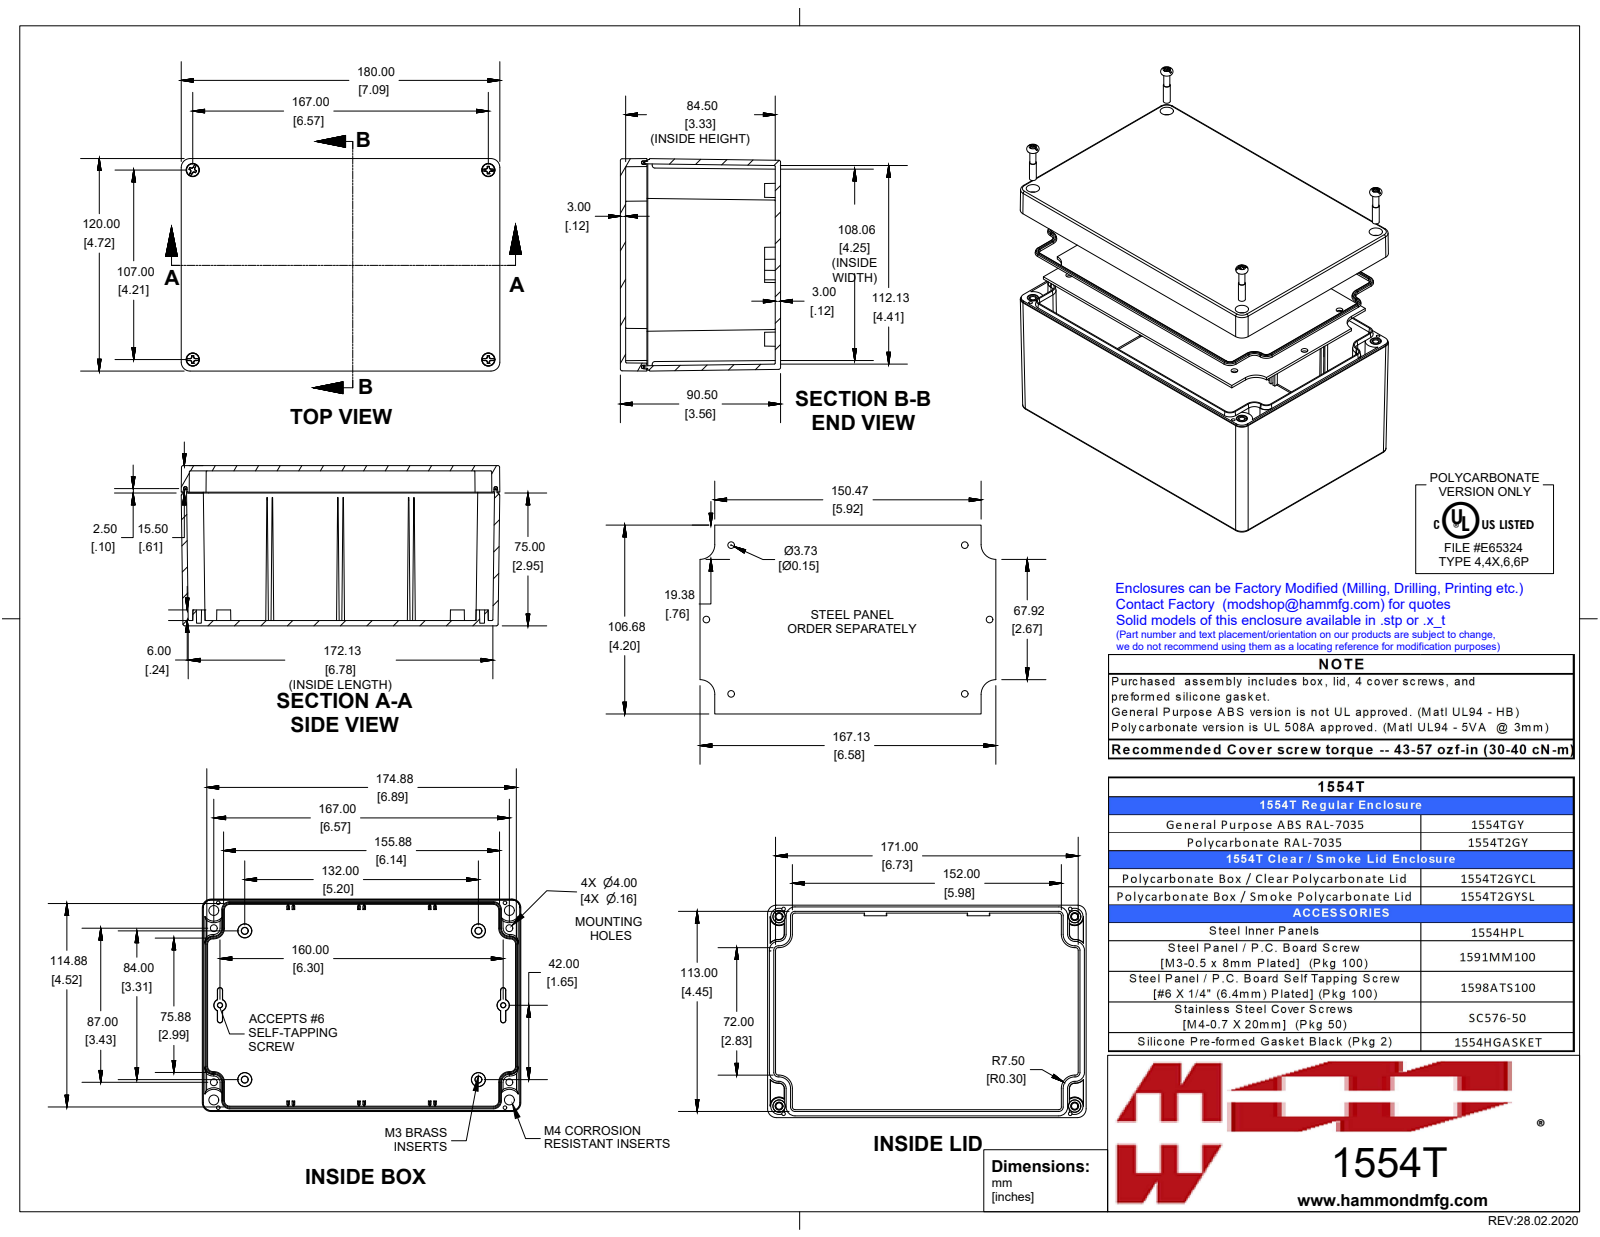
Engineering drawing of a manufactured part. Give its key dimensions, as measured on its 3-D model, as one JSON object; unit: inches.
{"part_name": "1554TGY", "step_written_by": "SolidWorks 2019 (AUTOMOTIVE_DESIGN)", "units": "inches", "bodies": {"solids": 15, "faces": 1364, "planar": 382, "cylindrical": 348, "other": 634}, "overall_size": [7.087, 4.724, 3.563], "volume_in3": 18.94, "surface_area_in2": 343.1, "round_holes": [[0.079, 4], [0.097, 4], [0.128, 4], [0.138, 4], [0.276, 4]], "round_bosses_or_shafts": [[0.25, 4], [0.218, 4], [0.21, 4], [0.19, 4], [0.154, 4], [0.153, 4], [0.15, 4], [0.135, 4]], "partial_cylinders_radius": [[0.02, 44], [0.039, 8], [0.197, 8], [0.187, 4], [0.059, 2]], "face_to_face_distances": [0.118, 3.445, 3.563, 3.327, 0.059, 0.177, 0.492, 0.374, 0.433, 1.575], "hole_center_spacings": [0.197, 0.824, 0.859, 3.822, 3.974, 4.384, 5.821, 5.903]}
